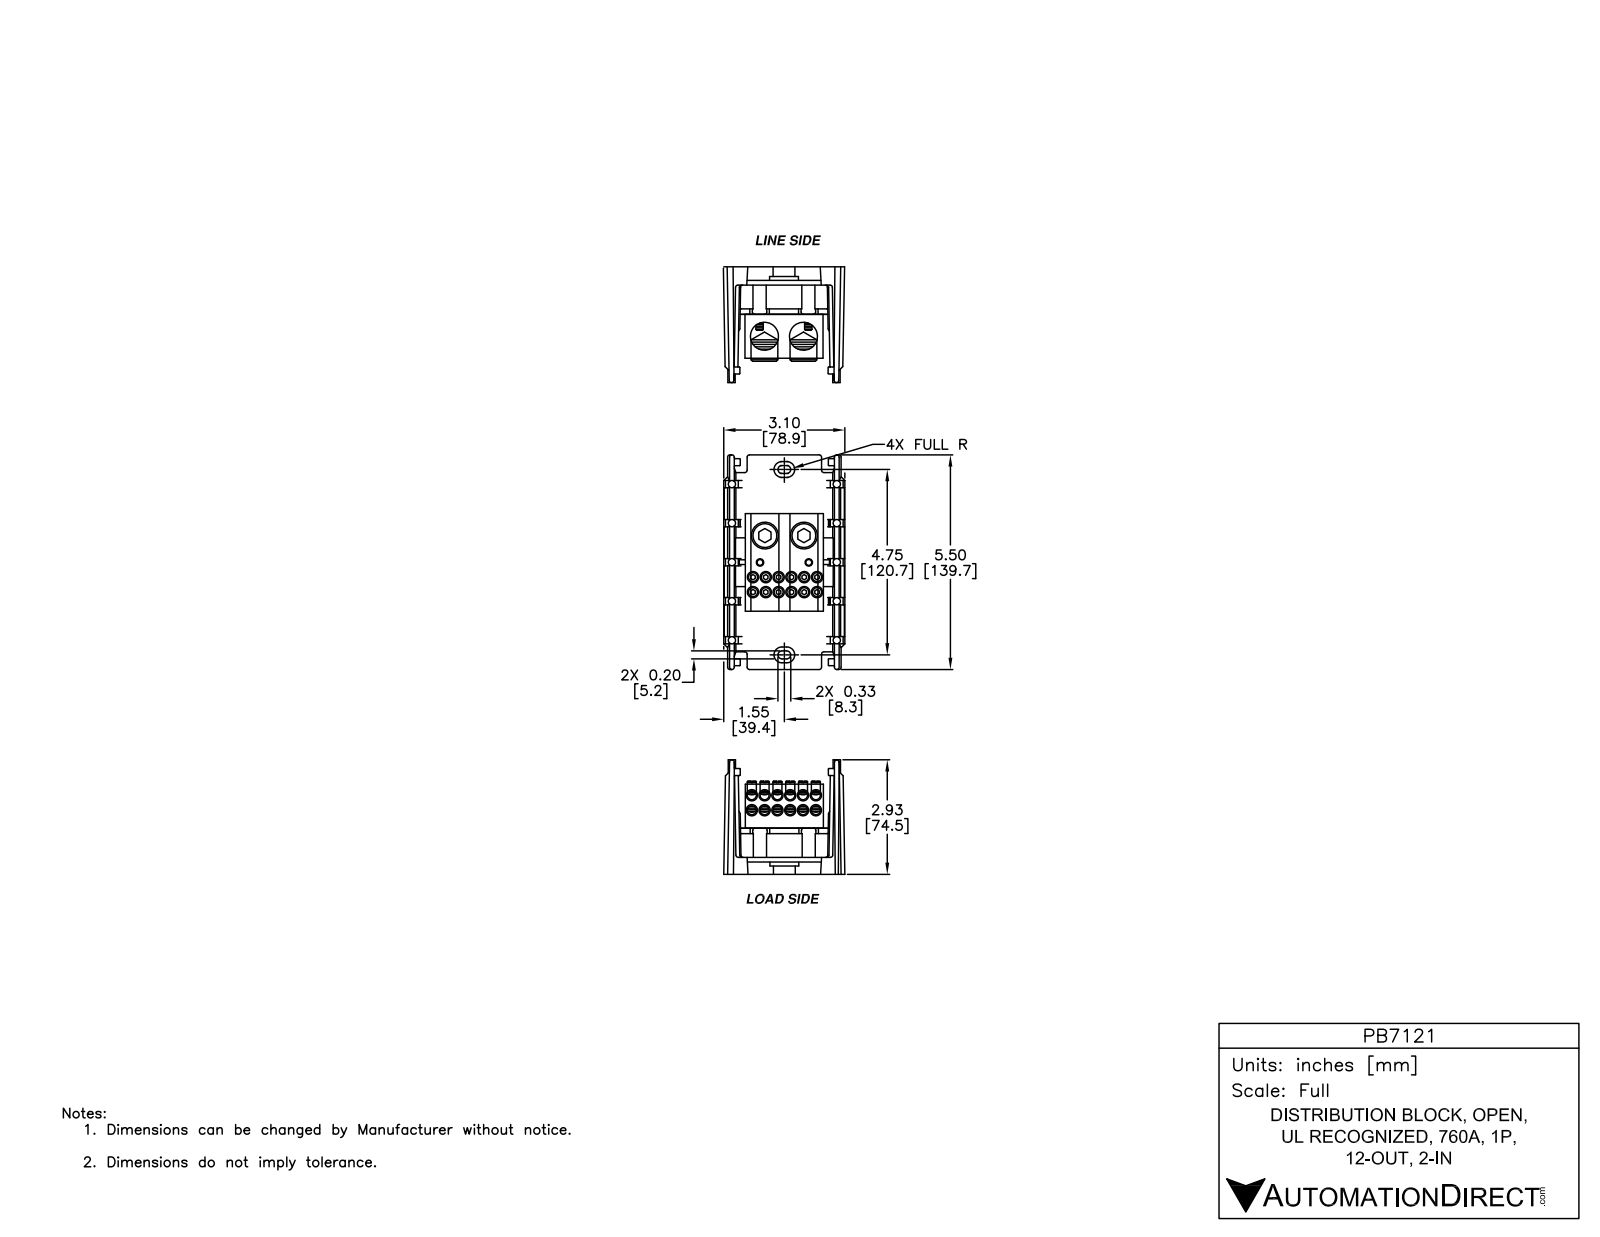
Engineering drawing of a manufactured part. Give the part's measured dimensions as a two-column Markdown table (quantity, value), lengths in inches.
| quantity | value |
| --- | --- |
| part name | PB7121 |
| STEP written by | SolidWorks 2014 (AUTOMOTIVE_DESIGN) |
| units | inches |
| bodies | 28 solids, 777 faces (473 planar, 268 cylindrical, 36 other) |
| overall size | 5.484 × 3.078 × 2.922 |
| volume | 13.72 in³ |
| surface area | 222 in² |
| round holes (diameter × count) | 0.25 × 14, 0.175 × 12, 0.219 × 12, 0.375 × 2, 0.75 × 2, 0.875 × 2 |
| round bosses / shafts (diameter × count) | 0.625 × 2, 0.187 × 2 |
| partial cylindrical surfaces (radius × count) | 0.031 × 8, 0.097 × 8, 0.203 × 8, 0.2 × 4, 0.312 × 3, 0.313 × 1 |
| main face-to-face distances | 2.703, 0.123, 0.125, 2.826, 2.58, 0.249, 2.577, 0.126, 2.454, 1.125 |
| hole center spacings | 0.75, 1, 0.375, 0.586, 0.704, 2, 0.375, 0.875 |
